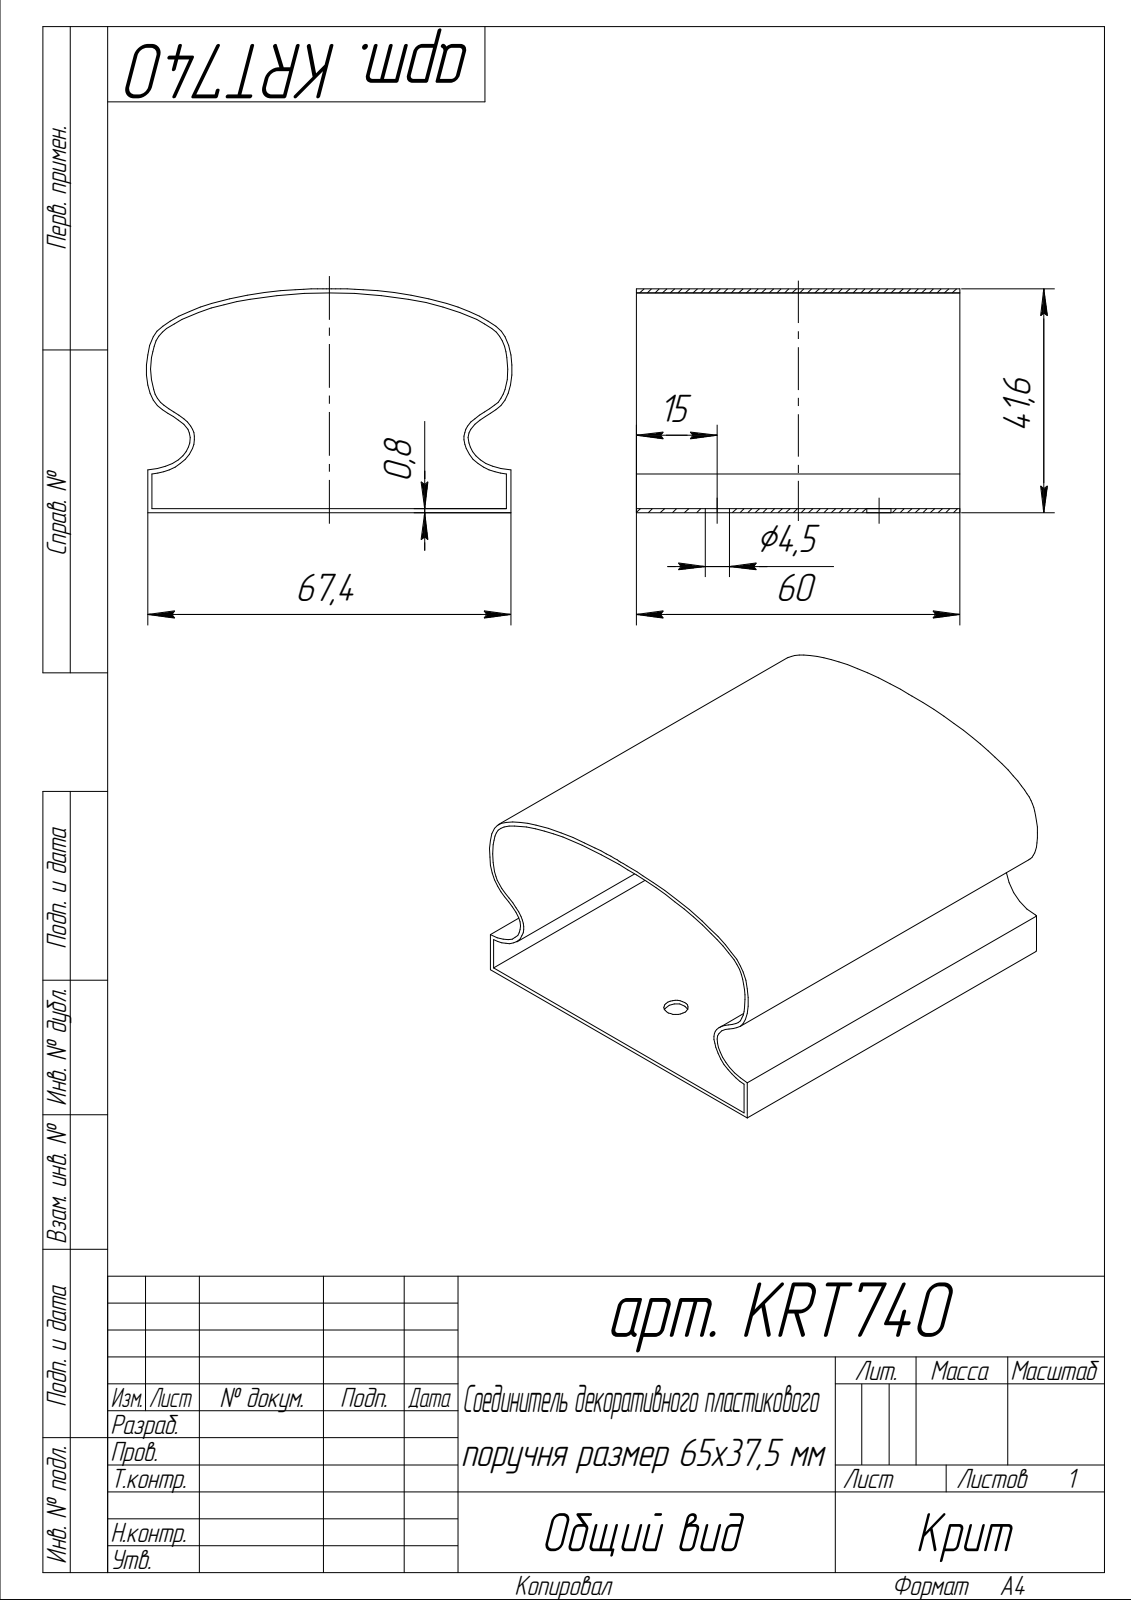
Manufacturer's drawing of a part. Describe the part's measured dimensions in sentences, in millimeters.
The part is named "арт. KRT740". Its 3-D file was written by "SolidWorks 2014 (AUTOMOTIVE_DESIGN)". It is 1 solid with 16 faces: 8 planar, 4 cylindrical and 4 other. Overall it measures 67.85 by 60 by 41.6 millimeters. Its volume is 11 673 cubic millimeters and its surface area 26 243 square millimeters. Round holes: 2 of diameter 4.5. The main face-to-face distances are 0.8, 66.6, 67.4, 65.8, 60. The hole center spacings are 30.
